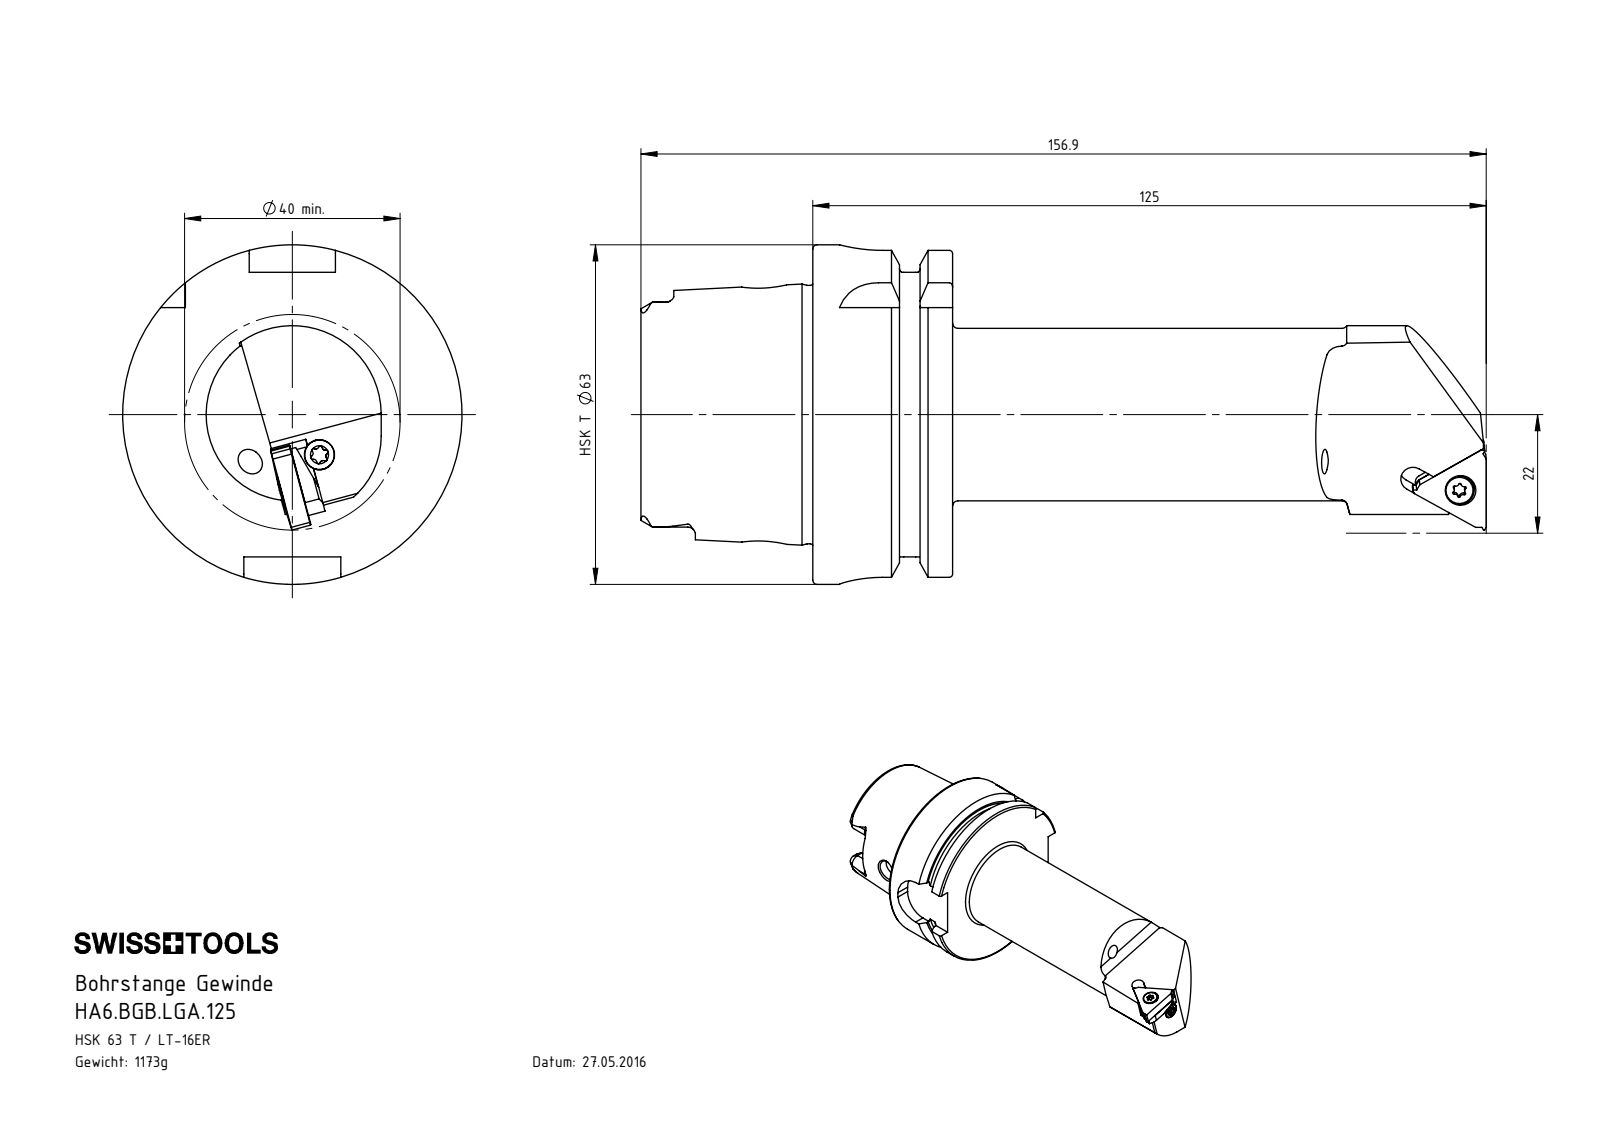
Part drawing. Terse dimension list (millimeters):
name: HA6-BGB.LGA.125; WGB-ER3.001.007_A; LT16ER; WGB-ER2.102.003_A (+2 more)
written by: SolidWorks 2012 (AUTOMOTIVE_DESIGN)
unit: mm
bodies: 5 solids, 332 faces (113 planar, 112 cylindrical, 107 other)
size: 156.9 × 63 × 63
volume: 148 998 mm³; area: 34 969 mm²
holes: 2× ⌀2.58, 2× ⌀4.2, 1× ⌀4, 1× ⌀4.02, 1× ⌀5, 1× ⌀7.5, 1× ⌀8.5, 1× ⌀10, 1× ⌀17, 1× ⌀19, 1× ⌀34, 1× ⌀40
bosses: 2× ⌀3.18, 1× ⌀63, 1× ⌀54.95, 1× ⌀47.94, 1× ⌀32, 1× ⌀5.5, 1× ⌀5.4, 1× ⌀2.78
rounds: 12× R0.23, 12× R0.57, 6× R1.4, 4× R2.88, 4× R8, 2× R0.1, 1× R0.25, 1× R1.3
face distances: 25.95, 16, 9.95, 31.9, 41.85, 57.85, 52.8, 21.8, 11.85, 53.7
hole spacings: 467.87, 467.92
